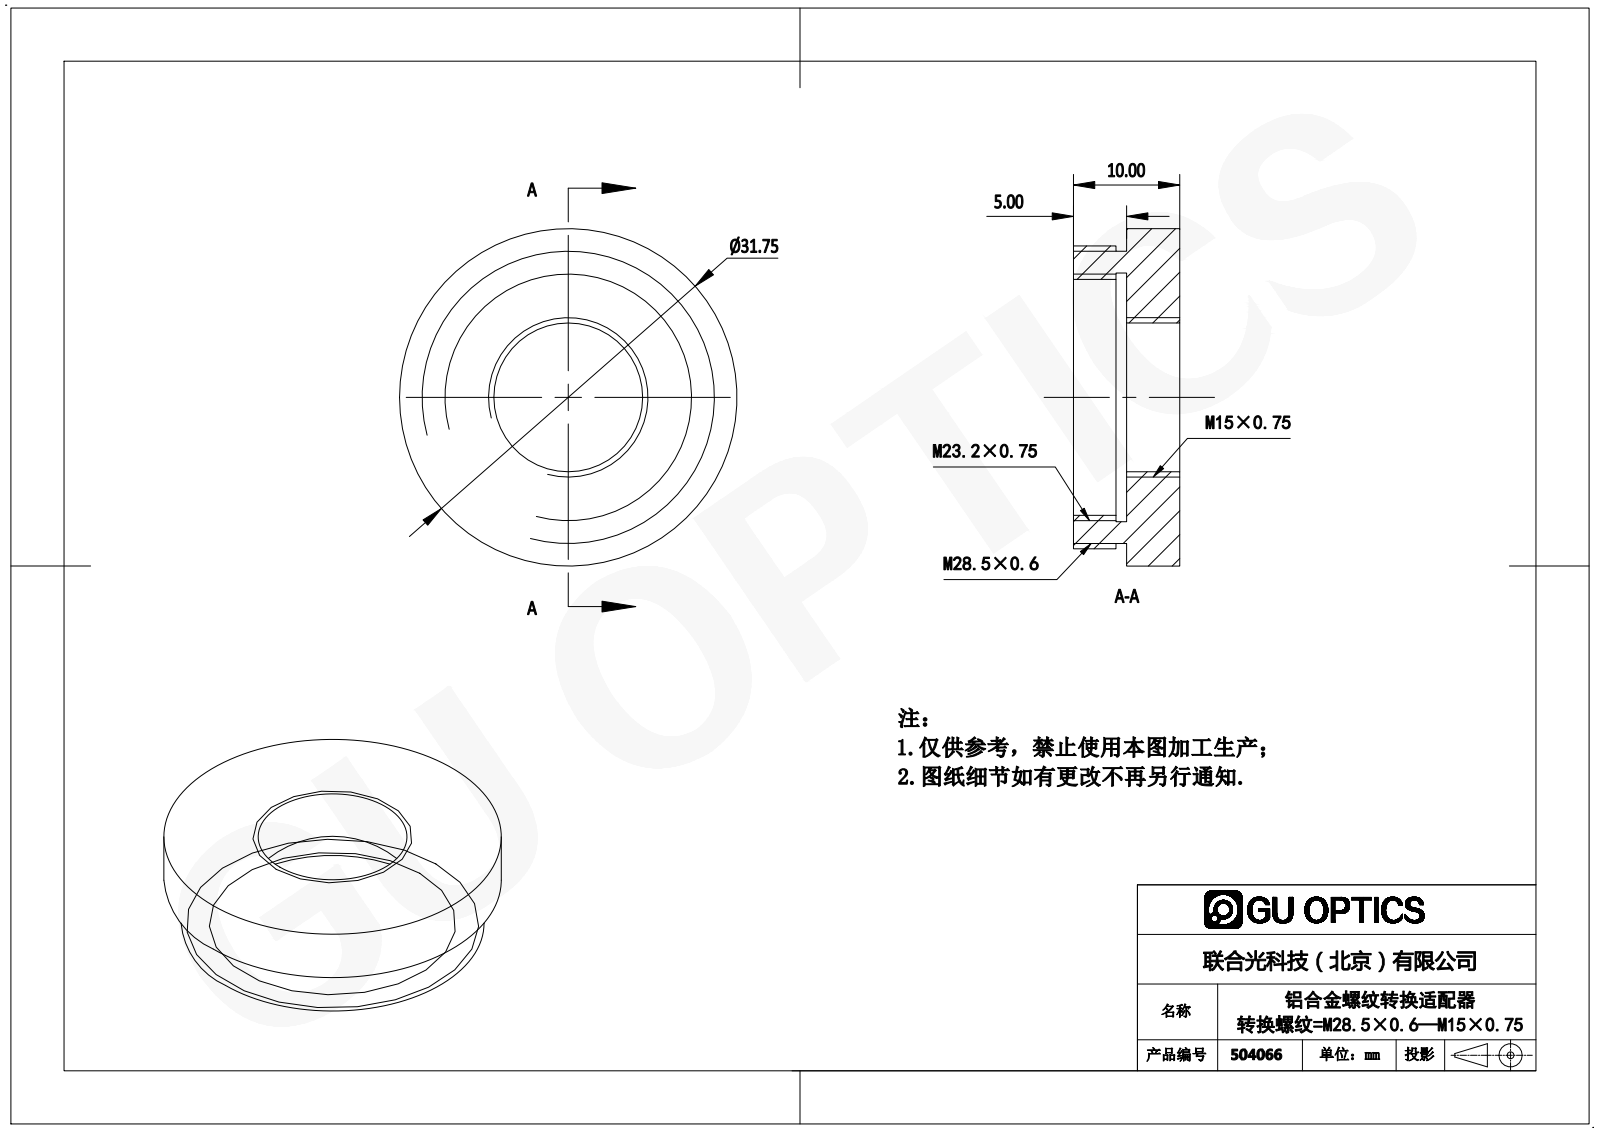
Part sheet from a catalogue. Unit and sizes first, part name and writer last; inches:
Units: inches
Overall size (bounding box): 1.25 × 1.25 × 0.394
Round holes (diameter × count): ⌀0.551 ×1, ⌀0.874 ×1, ⌀0.921 ×1
Round bosses / shafts (diameter × count): ⌀1.25 ×1, ⌀1.122 ×1, ⌀1.083 ×1
Main face-to-face distances: 0.197, 0.394, 0.157, 0.039, 0.236
Volume: 0.266 in³ · Surface area: 4.596 in²
Bodies: 1 solid, 18 faces (6 planar, 12 cylindrical, 0 other)
Part name (STEP PRODUCT): 504066
STEP written by: SolidWorks 2016 (AUTOMOTIVE_DESIGN)
